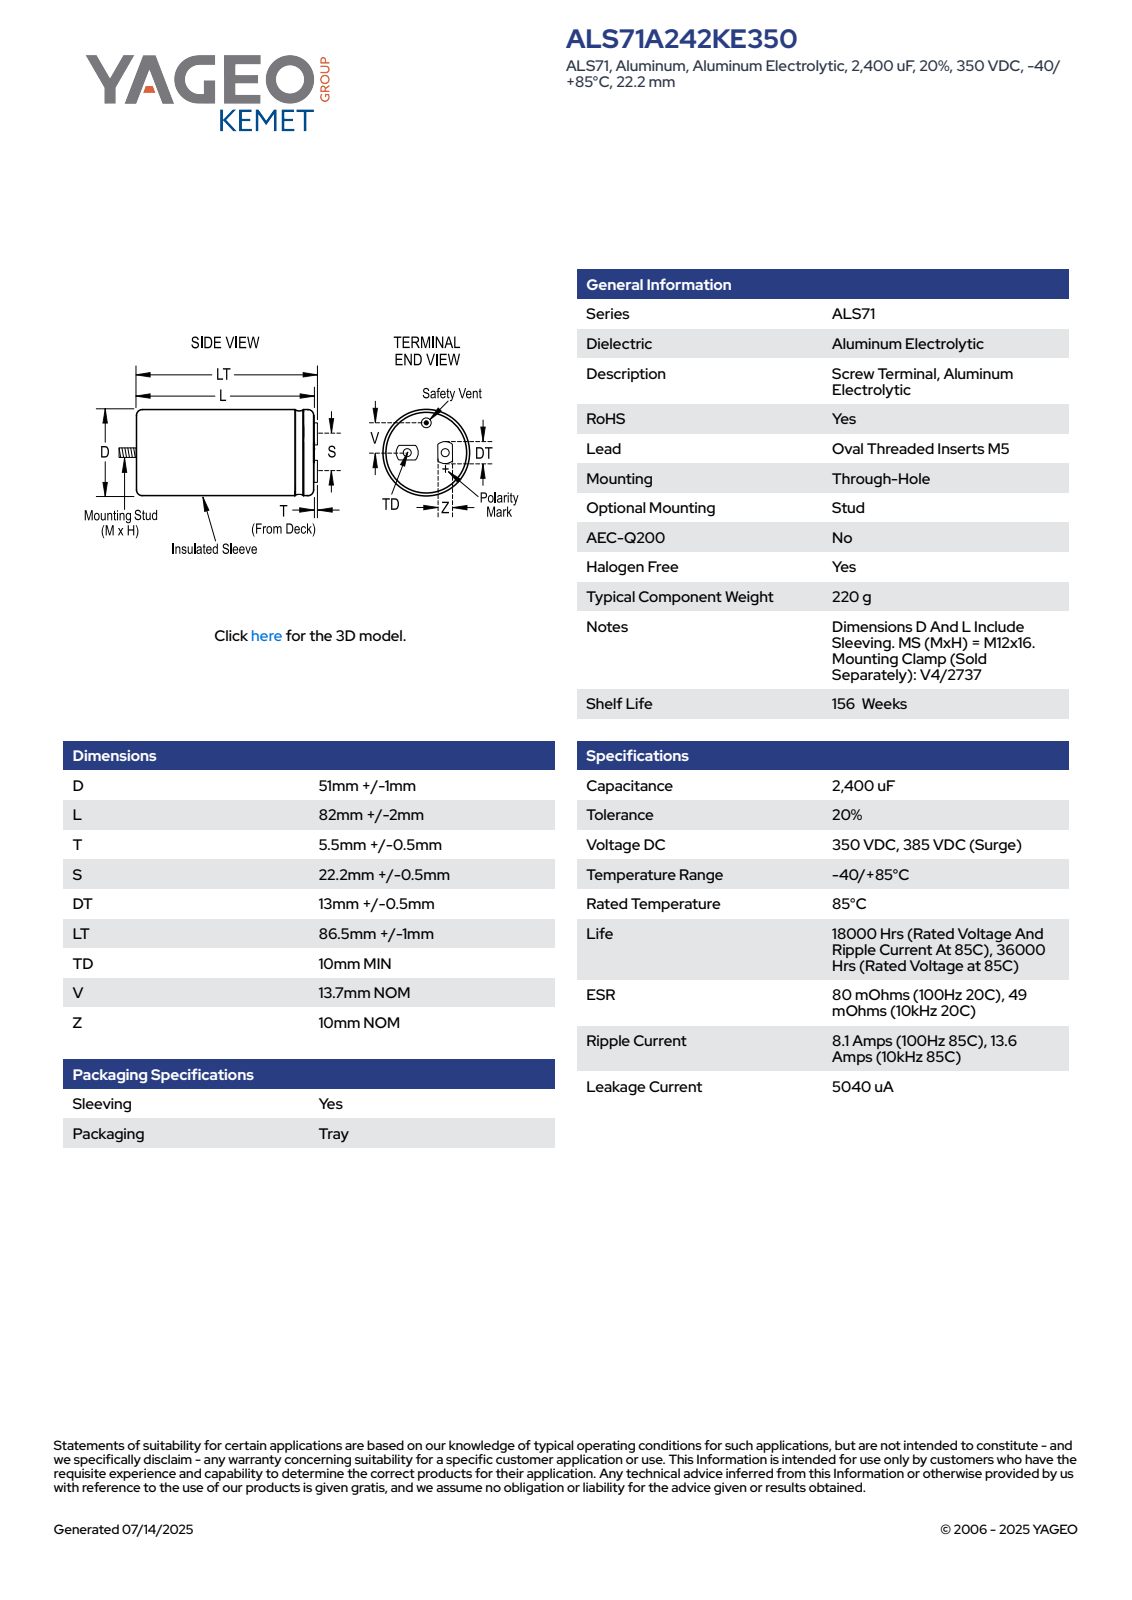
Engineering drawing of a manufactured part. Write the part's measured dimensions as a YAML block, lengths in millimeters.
part_name: "CARC_KALSOS_51X82_D52L84T6S22.2DT13.5TD10.000LT87.500V13.700"
step_written_by: "SolidWorks 2014 (AUTOMOTIVE_DESIGN)"
units: millimeters
bodies: {solids: 1, faces: 98, planar: 35, cylindrical: 24, other: 39}
overall_size: [103.5, 52, 52]
volume: 177845
surface_area: 19462
round_holes:
  - {diameter: 5, count: 2}
  - {diameter: 2, count: 1}
  - {diameter: 48, count: 1}
round_bosses_or_shafts:
  - {diameter: 52, count: 1}
  - {diameter: 12, count: 1}
  - {diameter: 3, count: 1}
partial_cylinders:
  - {radius: 8, count: 4}
  - {radius: 25.99, count: 1}
face_to_face_distances: [83, 87.5, 4.5, 10, 16, 99, 103.5, 93.5, 77.5, 5.5]
hole_center_spacings: [11.1, 17.63, 13.7, 22.2]
